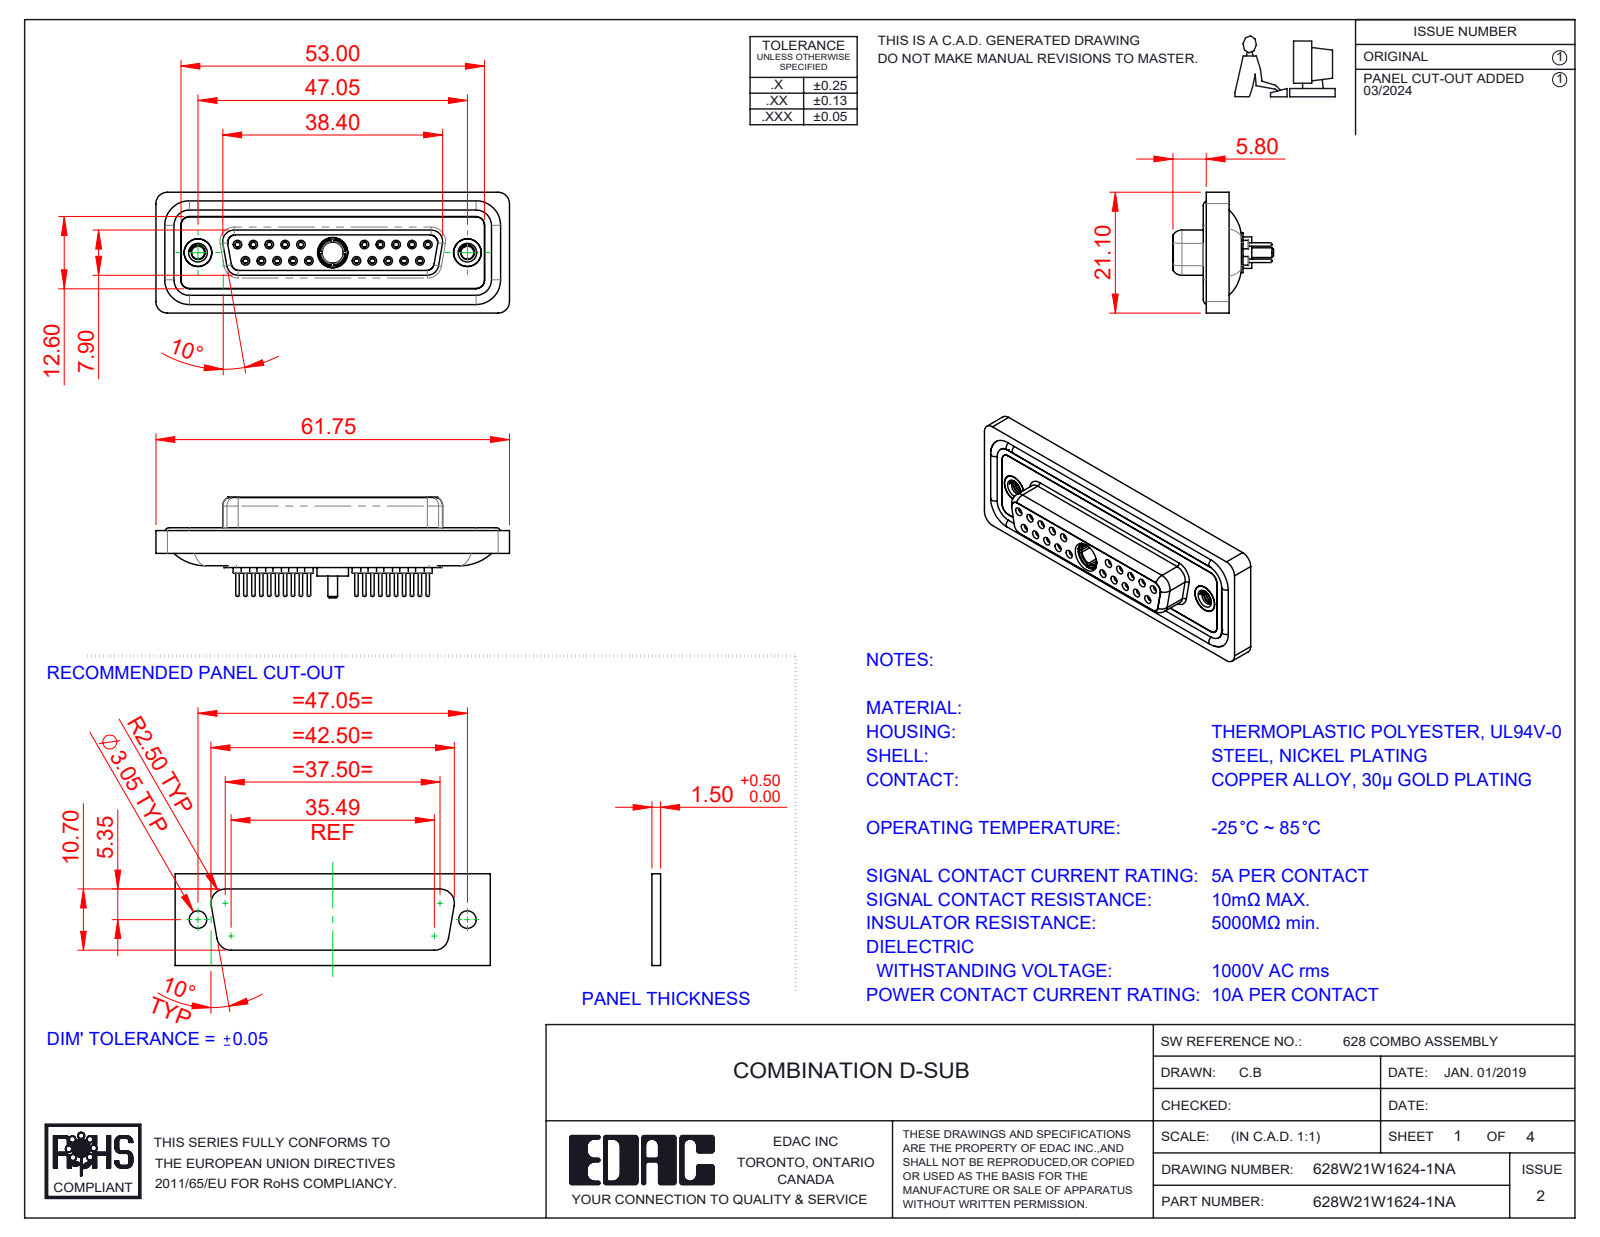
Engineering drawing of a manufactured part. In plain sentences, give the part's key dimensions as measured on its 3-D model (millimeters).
The part is named "628Combo Housing_21W1; 628W21W1624-1NA; 628Combo Waterproof Housing_25 Contacts; 628Combo Shell Rear_25 Contacts (+5 more)". Its 3-D file was written by "SolidWorks 2023 (CONFIG_CONTROL_DESIGN)". It is 29 solids with 1558 faces: 434 planar, 593 cylindrical and 531 other. Overall it measures 61.75 by 21.1 by 17.55 millimeters. Its volume is 8 361 cubic millimeters and its surface area 13 987 square millimeters. Round holes: 20 of diameter 0.9, 20 of diameter 1.1, 20 of diameter 1.5, 20 of diameter 2, 10 of diameter 1.6, 10 of diameter 1.7, 3 of diameter 4.85, 2 of diameter 2.26, 2 of diameter 4, 2 of diameter 4.05, 2 of diameter 5, 1 of diameter 3.7. Round bosses or shafts: 20 of diameter 2.2, 20 of diameter 0.6, 14 of diameter 1.6, 2 of diameter 4.95, 2 of diameter 4.8, 1 of diameter 5.5, 1 of diameter 5.2, 1 of diameter 4.96. Partial cylindrical surfaces (rounded edges, fillets, slot ends): 22 of radius 1.5, 18 of radius 2, 8 of radius 1.35, 8 of radius 1.6, 4 of radius 0.25, 4 of radius 0.5, 4 of radius 0.6, 4 of radius 0.65. The main face-to-face distances are 0.4, 1.8, 7.45, 6.6, 5.65, 0.5, 1.6, 7.05, 2.9, 1.1. The hole center spacings are 3.16, 2.77, 5.54, 5.03, 8.31, 7.48, 16.62, 19.39.
